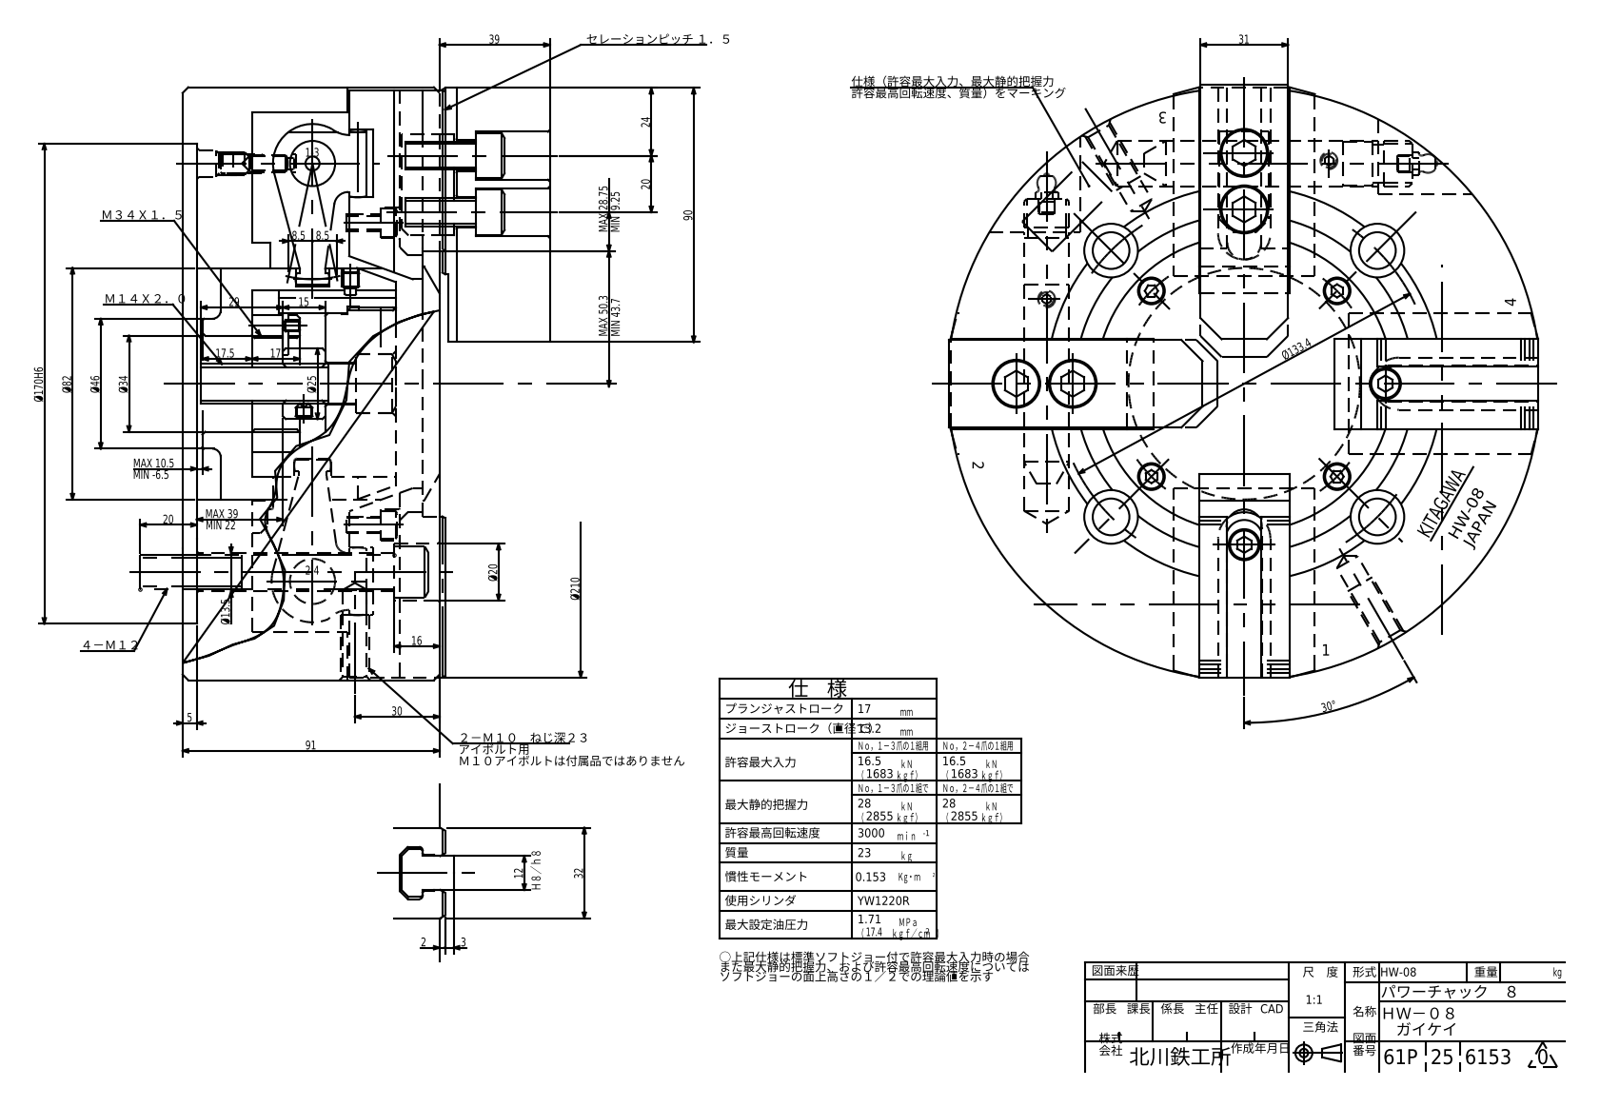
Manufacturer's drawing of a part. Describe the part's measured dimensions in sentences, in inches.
The part is named "HW08_mid stroke". Its 3-D file was written by "ST-DEVELOPER v16.7 (AUTOMOTIVE_DESIGN)". It is 44 solids with 4191 faces: 2934 planar, 938 cylindrical and 319 other. Overall it measures 8.268 by 8.268 by 5.717 inches. Its volume is 182.6 cubic inches and its surface area 856.8 square inches. Round holes: 12 of diameter 0.315, 9 of diameter 0.205, 9 of diameter 0.335, 8 of diameter 0.217, 8 of diameter 0.374, 8 of diameter 0.433, 8 of diameter 0.669, 4 of diameter 0.165, 4 of diameter 0.197, 4 of diameter 0.207, 4 of diameter 0.268, 4 of diameter 0.394. Round bosses or shafts: 8 of diameter 0.63, 8 of diameter 0.383, 4 of diameter 0.709, 4 of diameter 0.614, 4 of diameter 0.531, 4 of diameter 0.461, 4 of diameter 0.374, 4 of diameter 0.19. Partial cylindrical surfaces (rounded edges, fillets, slot ends): 156 of radius 0.004, 8 of radius 0.472, 4 of radius 0.157, 4 of radius 0.197, 4 of radius 0.248, 4 of radius 0.256, 4 of radius 0.364, 4 of radius 0.394. The main face-to-face distances are 0.02, 1.22, 0.394, 1.26, 0.63, 0.374, 1.024, 1.24, 2.126, 0.236. The hole center spacings are 0.866, 4.681, 0.394, 0.929, 1.08, 1.197, 1.418, 1.425.
